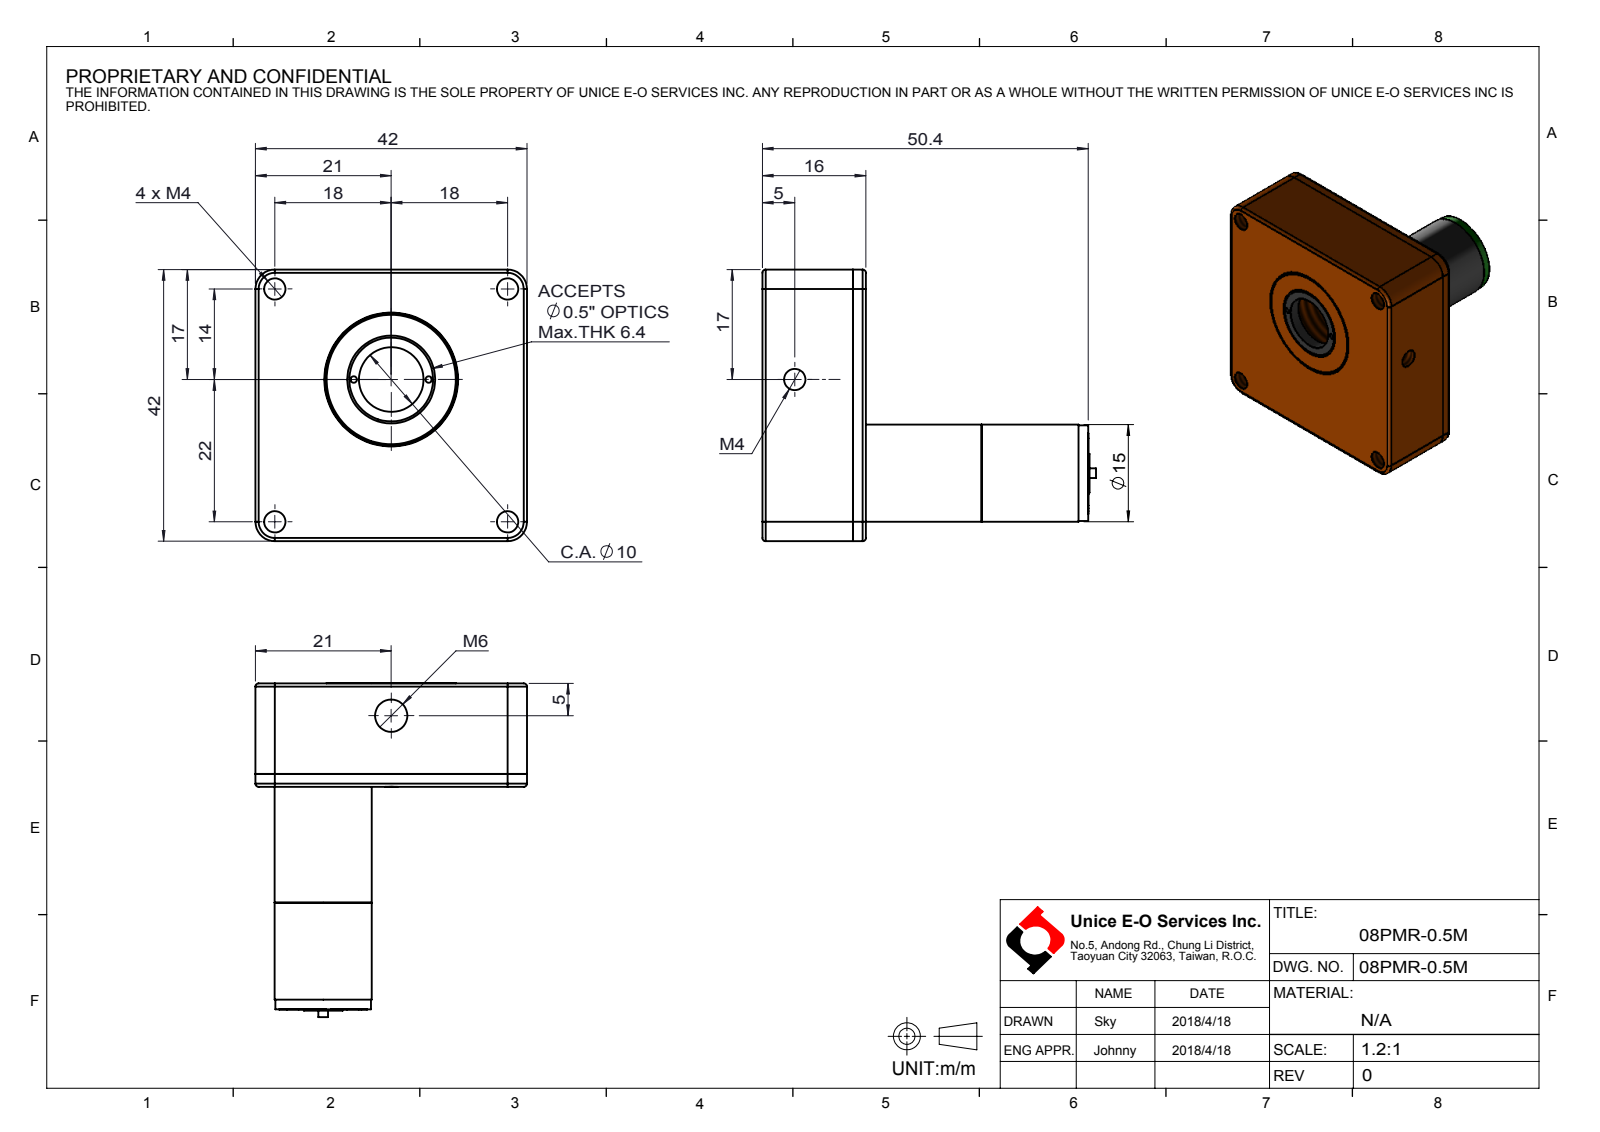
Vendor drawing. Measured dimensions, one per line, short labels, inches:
name: 08PMR-0.5M
written by: SolidWorks 2016 (AUTOMOTIVE_DESIGN)
unit: in
bodies: 0 solids, 195 faces (71 planar, 92 cylindrical, 32 other)
size: 2.032 × 1.654 × 1.654
holes: 5× ⌀0.13, 2× ⌀0.039, 1× ⌀0.067, 1× ⌀0.079, 1× ⌀0.197, 1× ⌀0.394, 1× ⌀0.51, 1× ⌀0.598, 1× ⌀0.807
bosses: 8× ⌀0.071, 3× ⌀0.228, 2× ⌀0.591, 1× ⌀0.787, 1× ⌀0.583, 1× ⌀0.236, 1× ⌀0.063, 1× ⌀0.059
rounds: 8× R0.02, 4× R0.118, 1× R0.295
face distances: 0.63, 1.654, 0.631, 0.705, 1.335, 1.335, 1.985, 1.355, 0.02, 0.724
hole spacings: 1.417, 0.228, 0.731, 0.898, 0.991, 1.087, 1.119, 1.276
